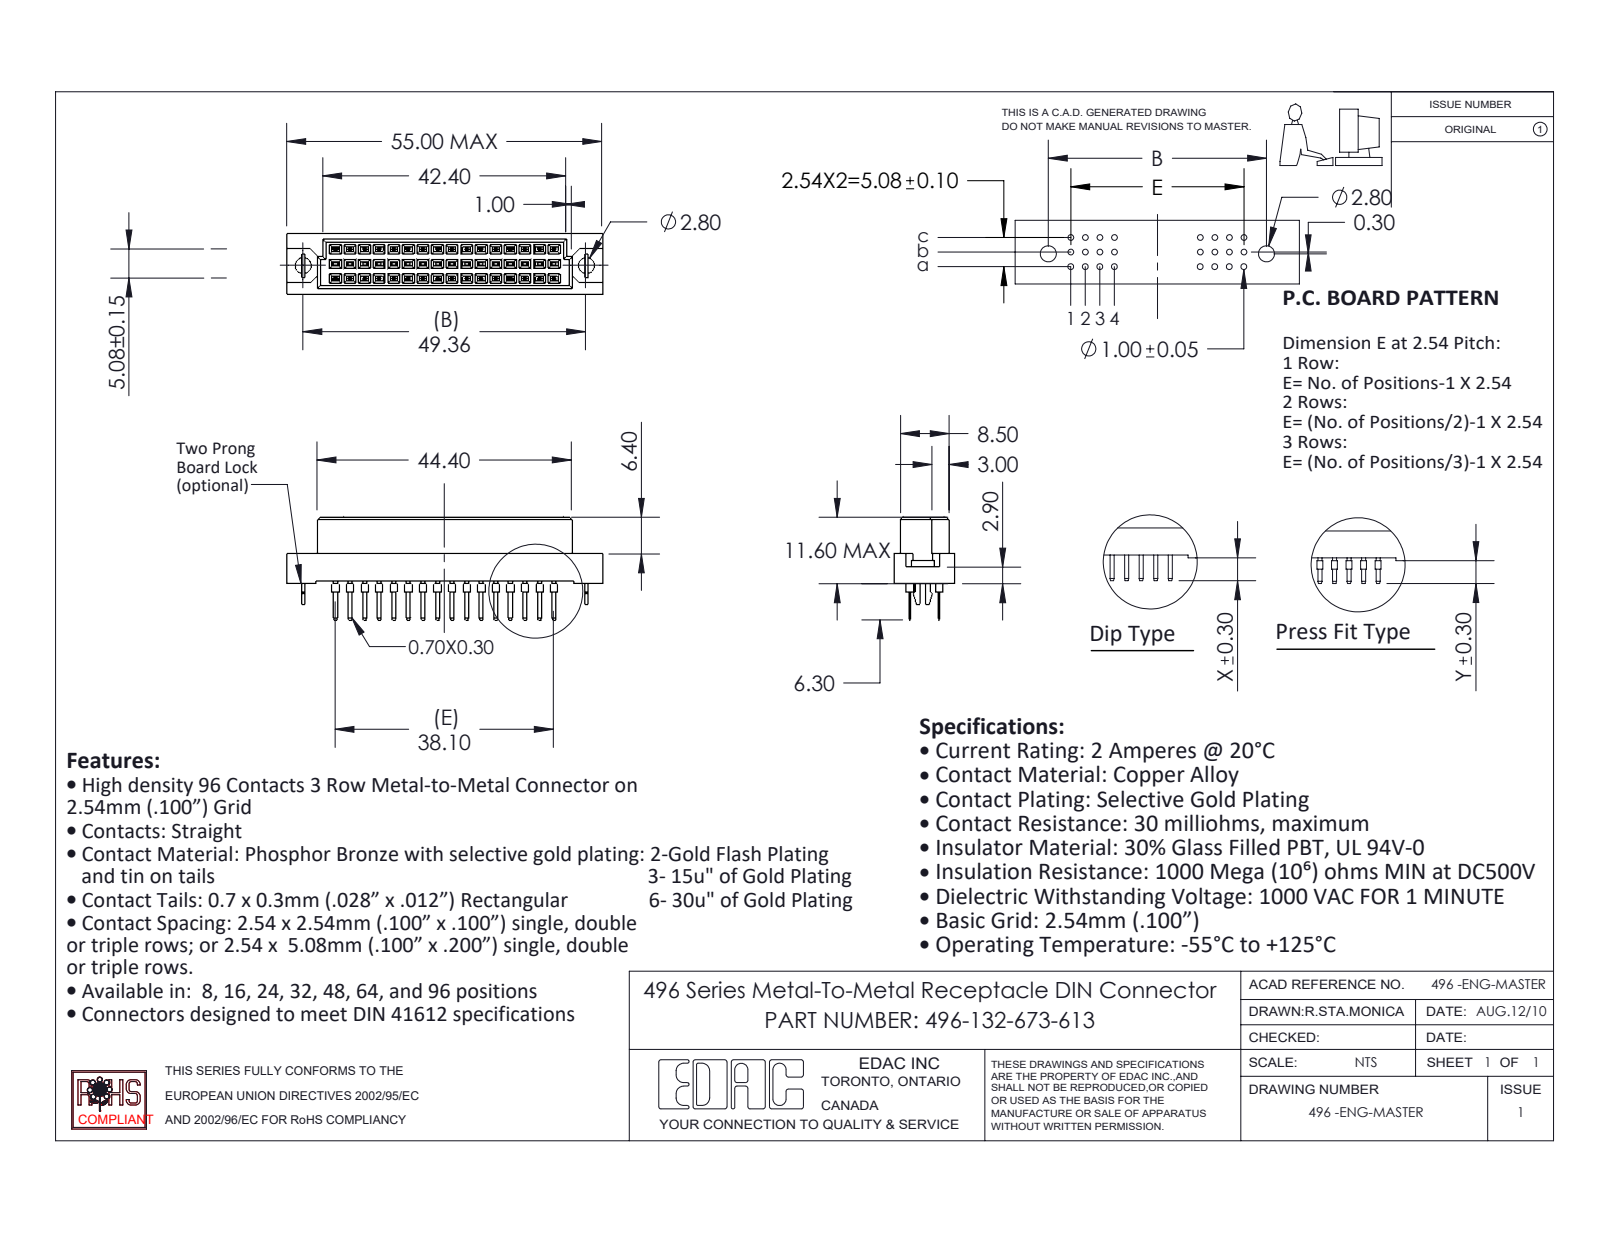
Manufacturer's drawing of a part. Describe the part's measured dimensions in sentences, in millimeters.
The part is named "496-132-673-613; 496-290_73; 496 Bore-lock; 496 Part_48". Its 3-D file was written by "SolidWorks 2020 (CONFIG_CONTROL_DESIGN)". It is 35 solids with 1278 faces: 1208 planar, 70 cylindrical and 0 other. Overall it measures 55 by 17.9 by 10.6 millimeters. Its volume is 4 710 cubic millimeters and its surface area 5 101 square millimeters. Round holes: 2 of diameter 2.8. Round bosses or shafts: 32 of diameter 1. Partial cylindrical surfaces (rounded edges, fillets, slot ends): 1 of radius 0.53. The main face-to-face distances are 2.54, 5.08, 1.05, 9.55, 0.81, 0.56, 0.55, 1.56, 1.86, 2.61. The hole center spacings are 49.36.
